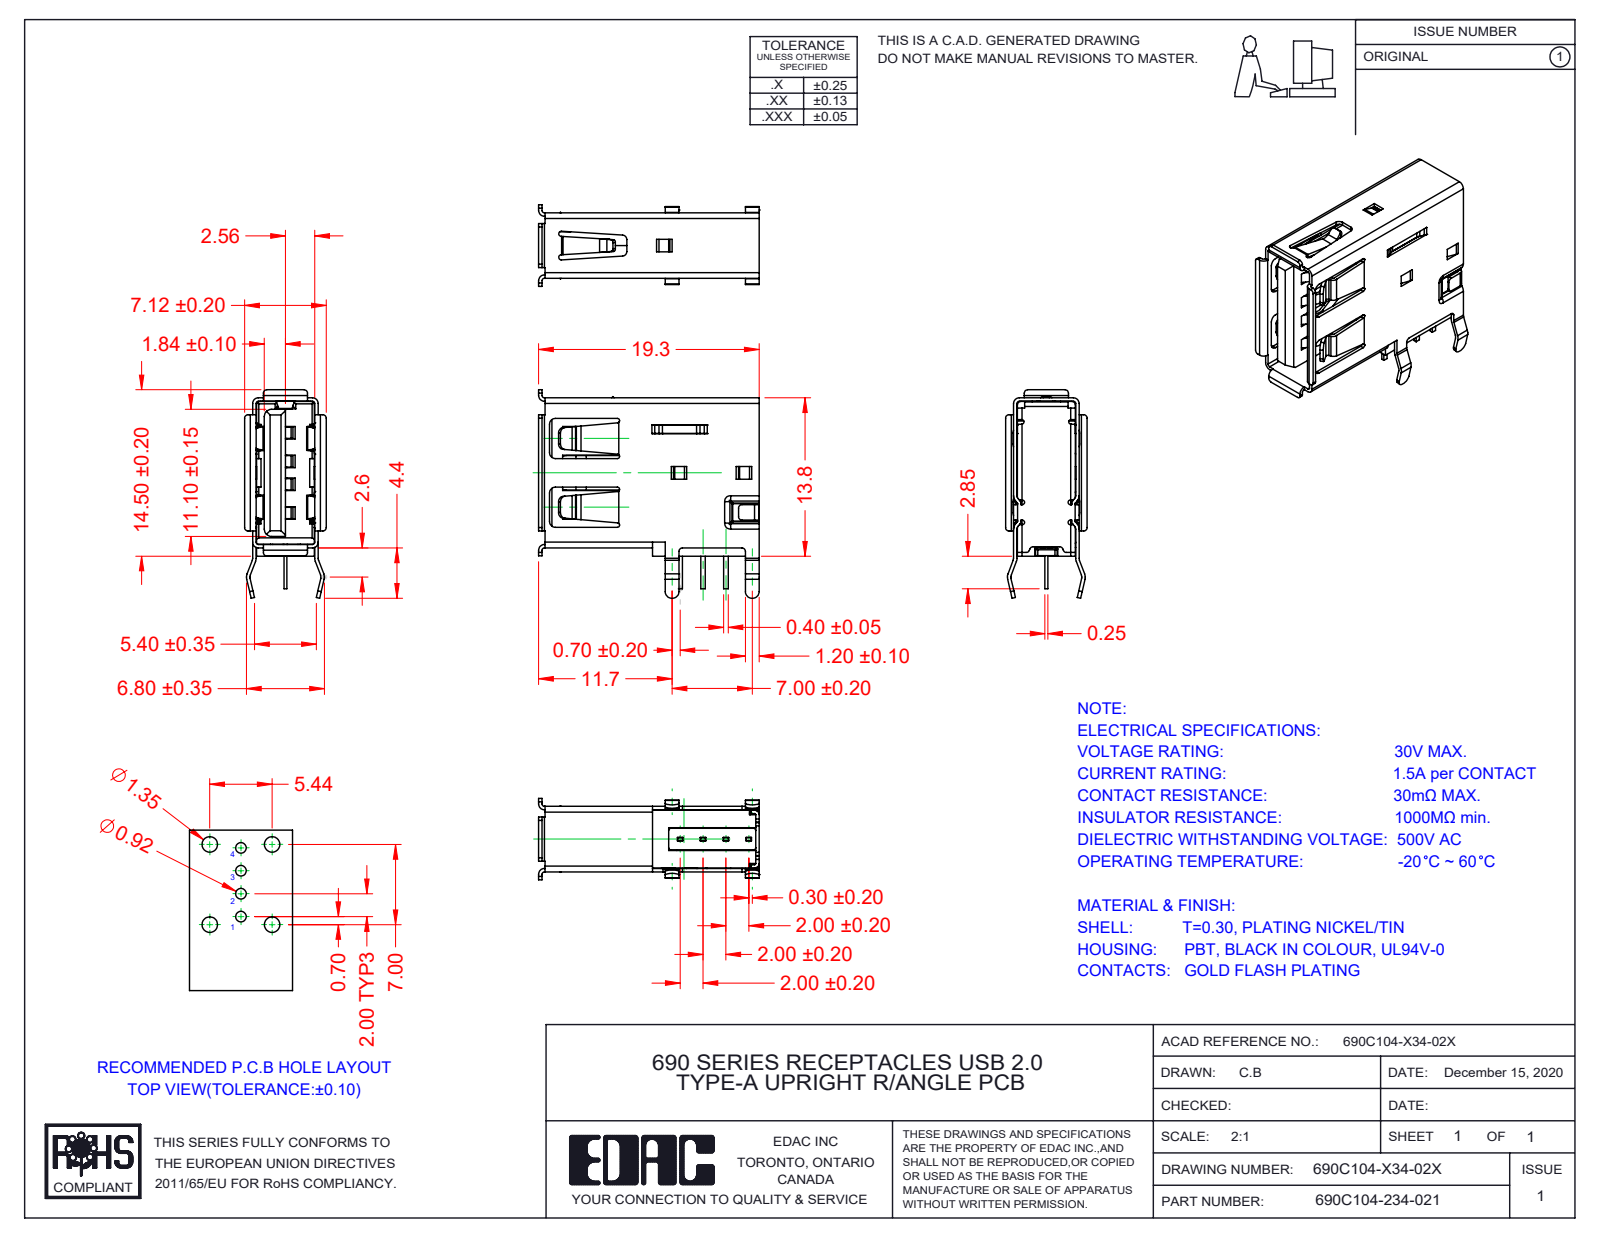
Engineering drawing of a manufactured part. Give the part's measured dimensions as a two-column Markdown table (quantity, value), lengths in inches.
| quantity | value |
| --- | --- |
| part name | Insulator2 690C104-X34-02X_White; 690C104-134-021; Contacts_3 690C104-X34-02X; Contacts 690C104-X34-02X (+5 more) |
| STEP written by | SolidWorks 2020 (AUTOMOTIVE_DESIGN) |
| units | inches |
| bodies | 7 solids, 1141 faces (753 planar, 332 cylindrical, 56 other) |
| overall size | 0.758 × 0.717 × 0.28 |
| volume | 0.04 in³ |
| surface area | 4.236 in² |
| partial cylindrical surfaces (radius × count) | 0.012 × 48, 0.008 × 33, 0.02 × 27, 0.016 × 24, 0.024 × 22, 0.006 × 18, 0.004 × 15, 0.028 × 11 |
| main face-to-face distances | 0.213, 0.225, 0.202, 0.504, 0.04, 0.113, 0.101, 0.185, 0.028, 0.098 |
